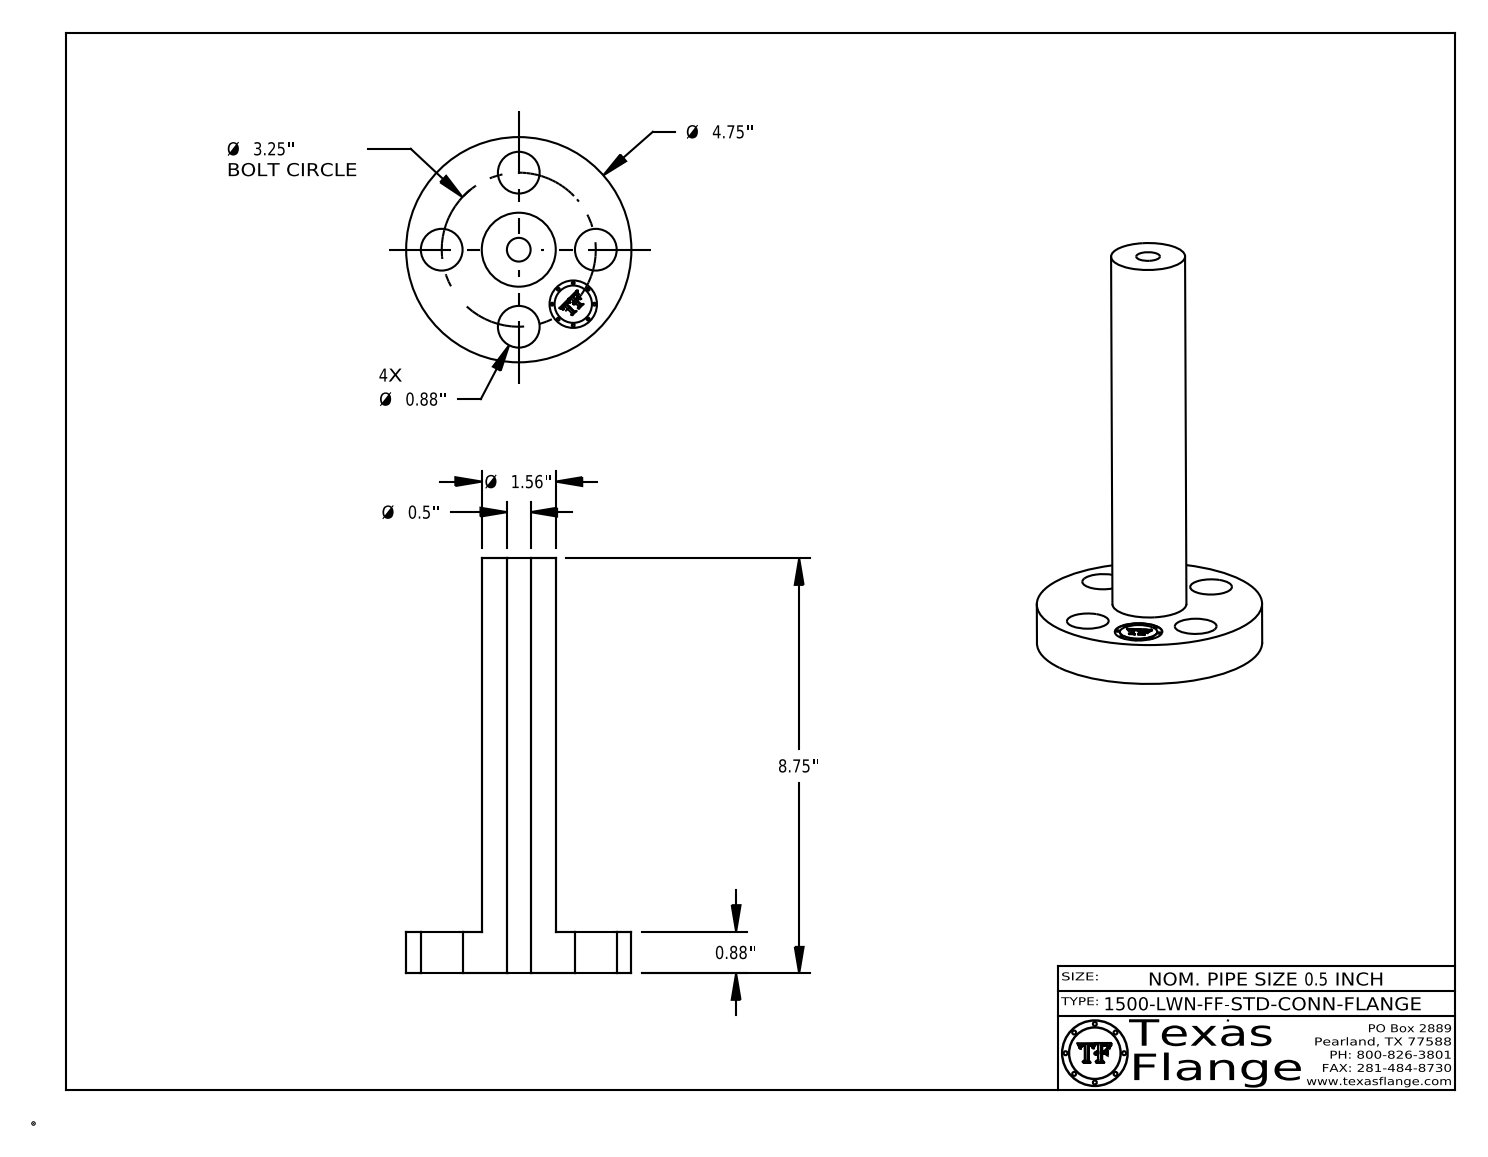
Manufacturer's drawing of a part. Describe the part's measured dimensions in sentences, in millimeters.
The part is named "0.5-1500-LWN-FF-STD-CONN-FLANGE". Its 3-D file was written by "CATIA V5 STEP AP214 (AUTOMOTIVE_DESIGN)". It is 1 solid with 402 faces: 368 planar, 34 cylindrical and 0 other. Overall it measures 222.3 by 120.7 by 120.7 millimeters. Its volume is 438 800 cubic millimeters and its surface area 68 000 square millimeters. Round holes: 4 of diameter 22.4, 1 of diameter 12.7, 1 of diameter 25.4. Round bosses or shafts: 8 of diameter 1.5, 1 of diameter 120.7, 1 of diameter 39.6, 1 of diameter 20. The main face-to-face distances are 22.4, 222.3, 199.9, 22.2, 200, 7.6, 7.4, 1.4, 4.9, 6.3. The hole center spacings are 41.3, 58.4, 31.6, 76.3, 82.6.
